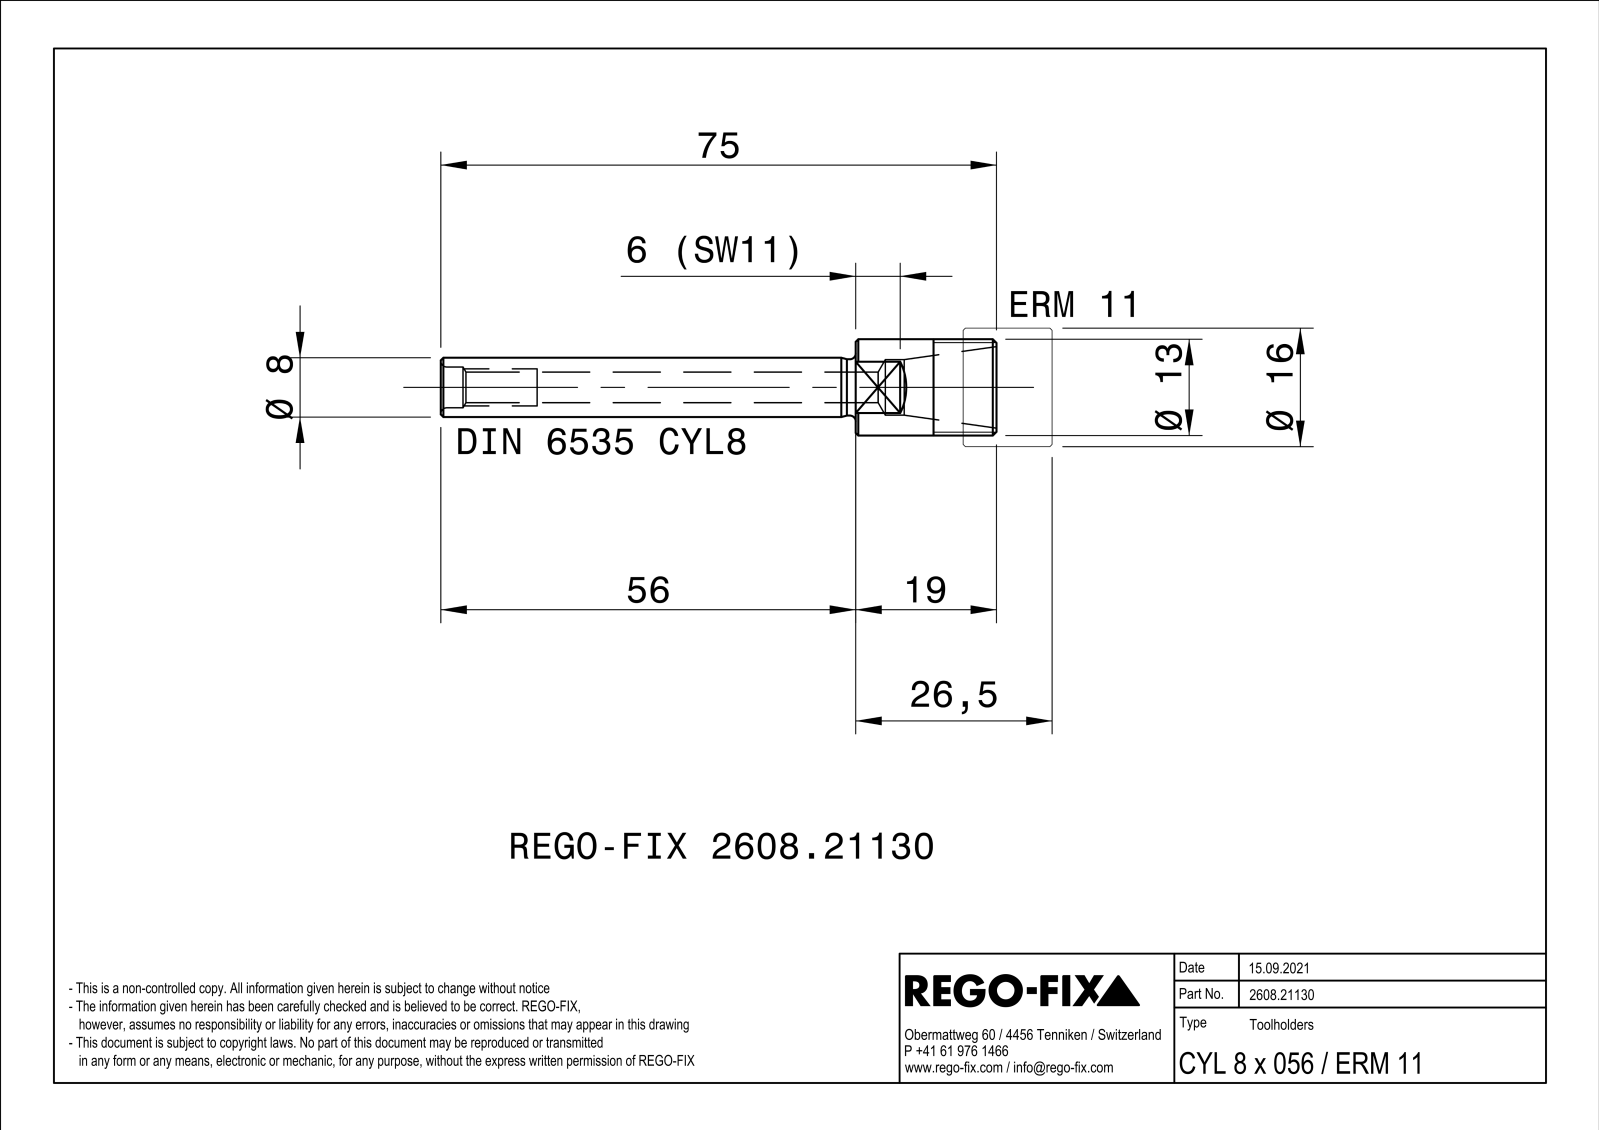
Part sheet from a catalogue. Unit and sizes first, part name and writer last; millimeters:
Units: millimetres
Overall size (bounding box): 75 × 13 × 13
Round holes (diameter × count): ⌀4.13 ×1, ⌀5.5 ×1, ⌀7.5 ×1
Round bosses / shafts (diameter × count): ⌀13 ×1, ⌀8 ×1, ⌀7.6 ×1
Main face-to-face distances: 11, 19, 4.03, 75, 56
Volume: 3 450 mm³ · Surface area: 3 528 mm²
Bodies: 1 solid, 28 faces (9 planar, 8 cylindrical, 11 other)
Part name (STEP PRODUCT): NOCUT
STEP written by: SIEMENS PLM Software Solid Edge ST10 (AUTOMOTIVE_DESIGN)
